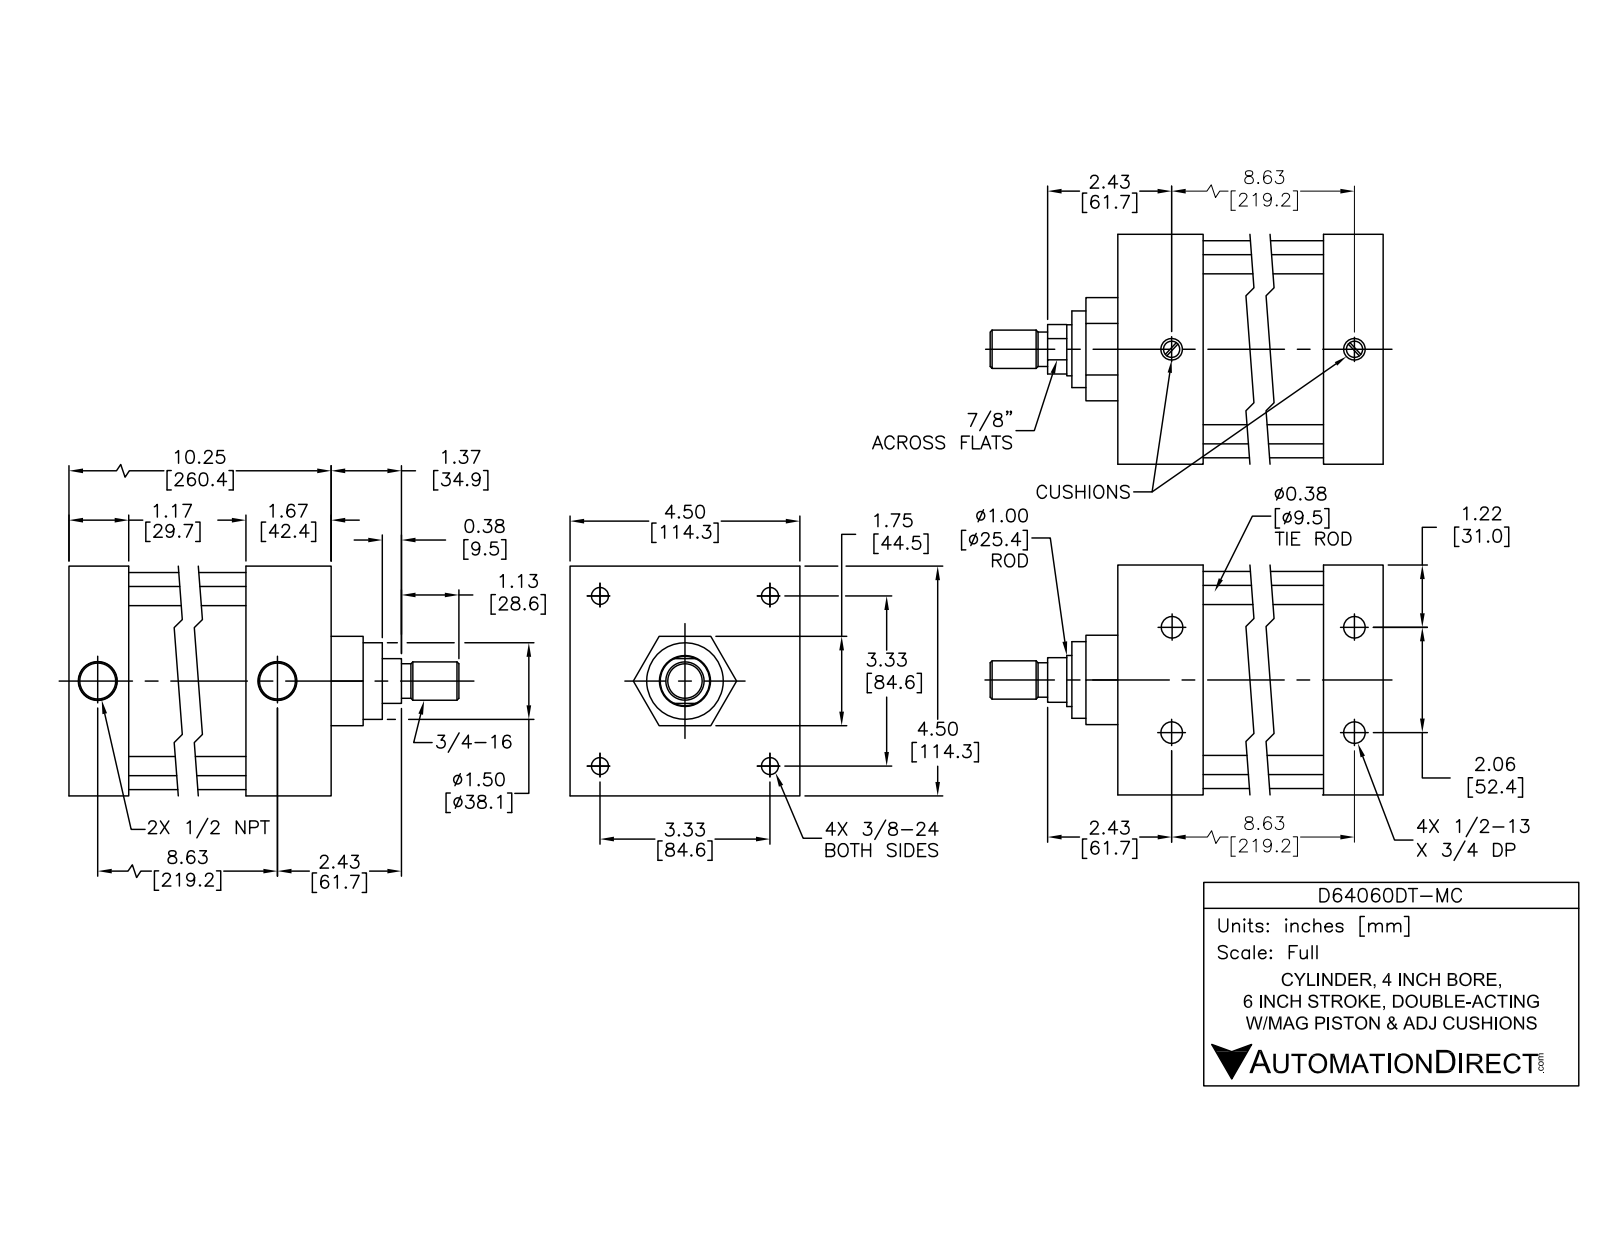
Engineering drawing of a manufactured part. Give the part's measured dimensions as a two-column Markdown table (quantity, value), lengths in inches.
| quantity | value |
| --- | --- |
| part name | D64060DT-M BODY; D64060DT-MC; D64060DT-M PISTON |
| STEP written by | SolidWorks 2015 (AUTOMOTIVE_DESIGN) |
| units | inches |
| bodies | 12 solids, 303 faces (99 planar, 114 cylindrical, 90 other) |
| overall size | 12.745 × 4.5 × 4.5 |
| volume | 93.93 in³ |
| surface area | 490.3 in² |
| round holes (diameter × count) | 0.33 × 4, 0.406 × 4, 0.417 × 4, 0.625 × 4, 0.5 × 2, 0.766 × 2, 1 × 1, 1.003 × 1, 4 × 1 |
| round bosses / shafts (diameter × count) | 0.609 × 4, 0.375 × 4, 0.34 × 4, 4.25 × 1, 3.997 × 1, 1.75 × 1, 0.997 × 1, 0.97 × 1 |
| partial cylindrical surfaces (radius × count) | 0.45 × 4 |
| main face-to-face distances | 4.5, 0.08, 7.326, 10.246, 1.75, 8.997, 1.249, 7.751, 1.246, 2.495 |
| hole center spacings | 2.349, 3.322, 8.683, 8.622, 1.031, 1.031, 2.062, 4.698 |
